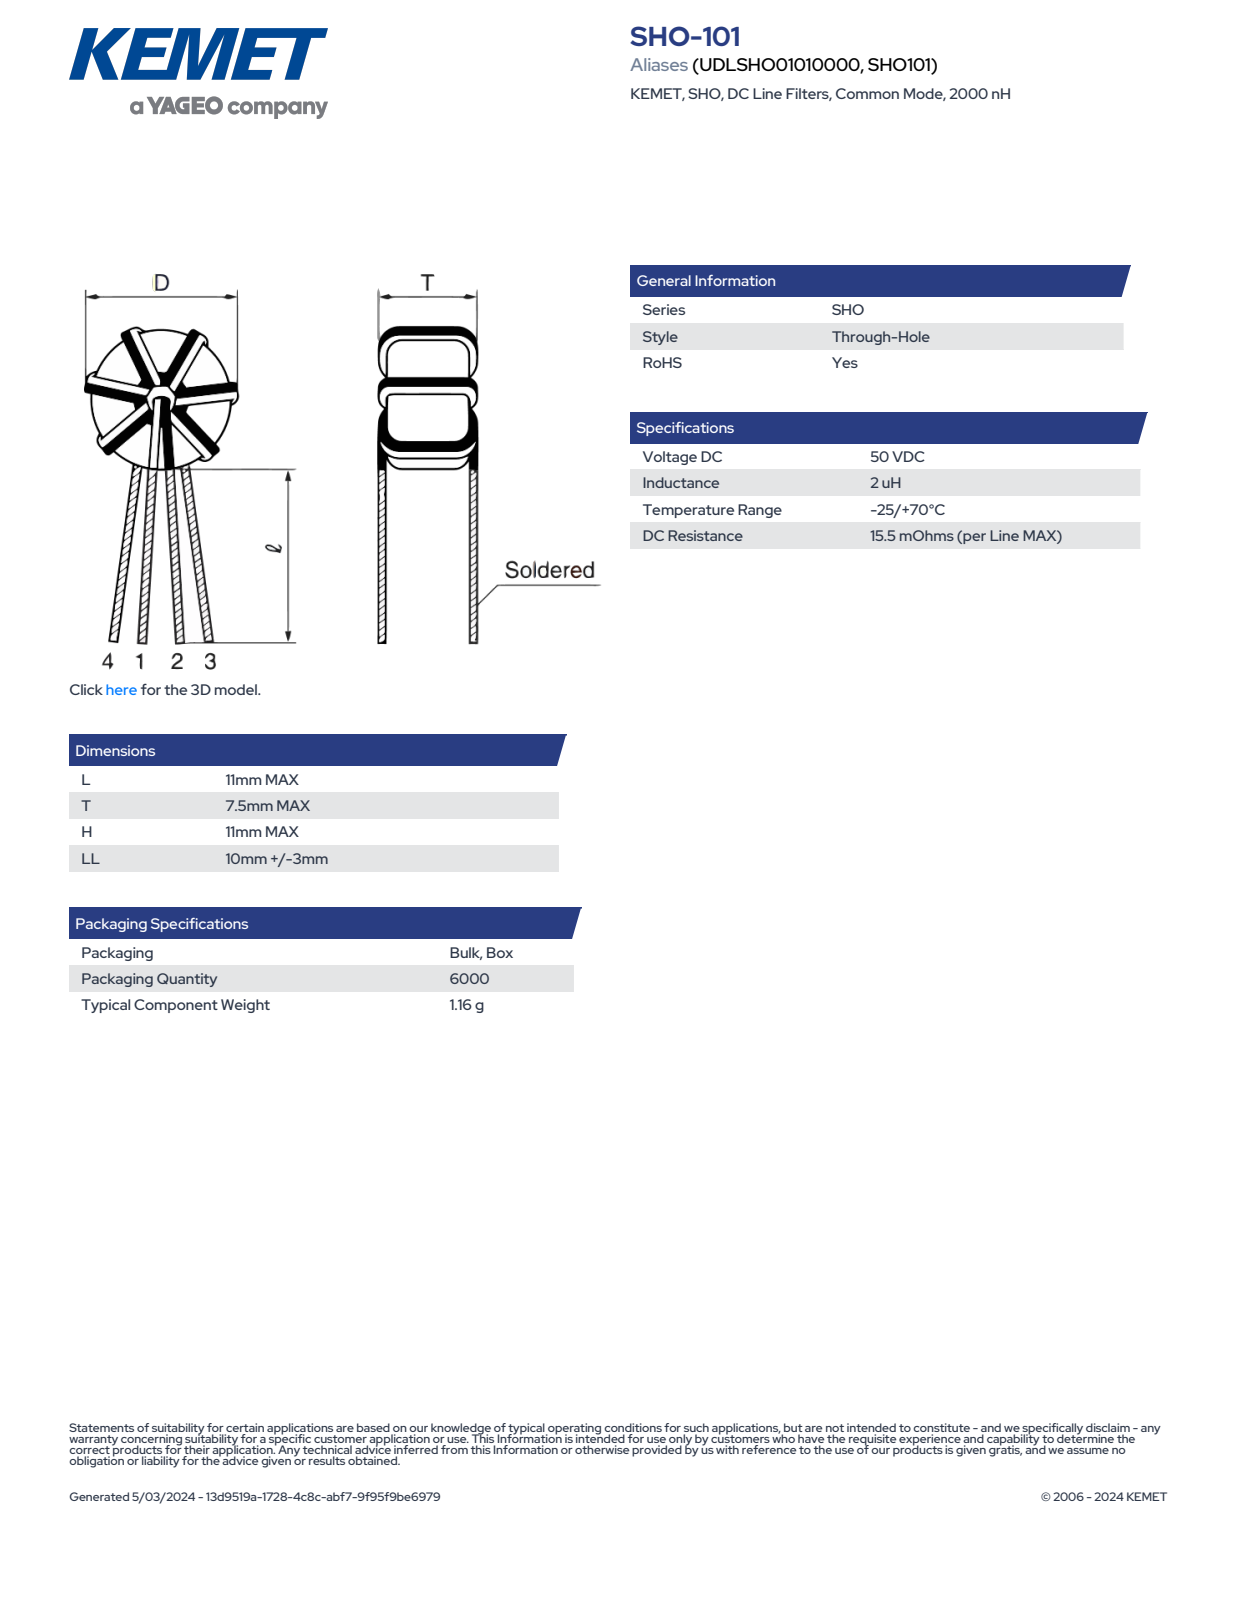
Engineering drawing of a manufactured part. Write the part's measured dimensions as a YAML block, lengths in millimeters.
part_name: "IFC_NTSHO_L11T7.5LL13"
step_written_by: "SolidWorks 2014 (AUTOMOTIVE_DESIGN)"
units: millimeters
bodies: {solids: 17, faces: 398, planar: 6, cylindrical: 264, other: 128}
overall_size: [23.65, 11, 7.5]
volume: 533
surface_area: 821
round_holes:
  - {diameter: 3.4, count: 1}
round_bosses_or_shafts:
  - {diameter: 0.3, count: 48}
  - {diameter: 0.3, count: 4}
  - {diameter: 10.3, count: 1}
partial_cylinders:
  - {radius: 0.15, count: 16}
face_to_face_distances: [6.8]
